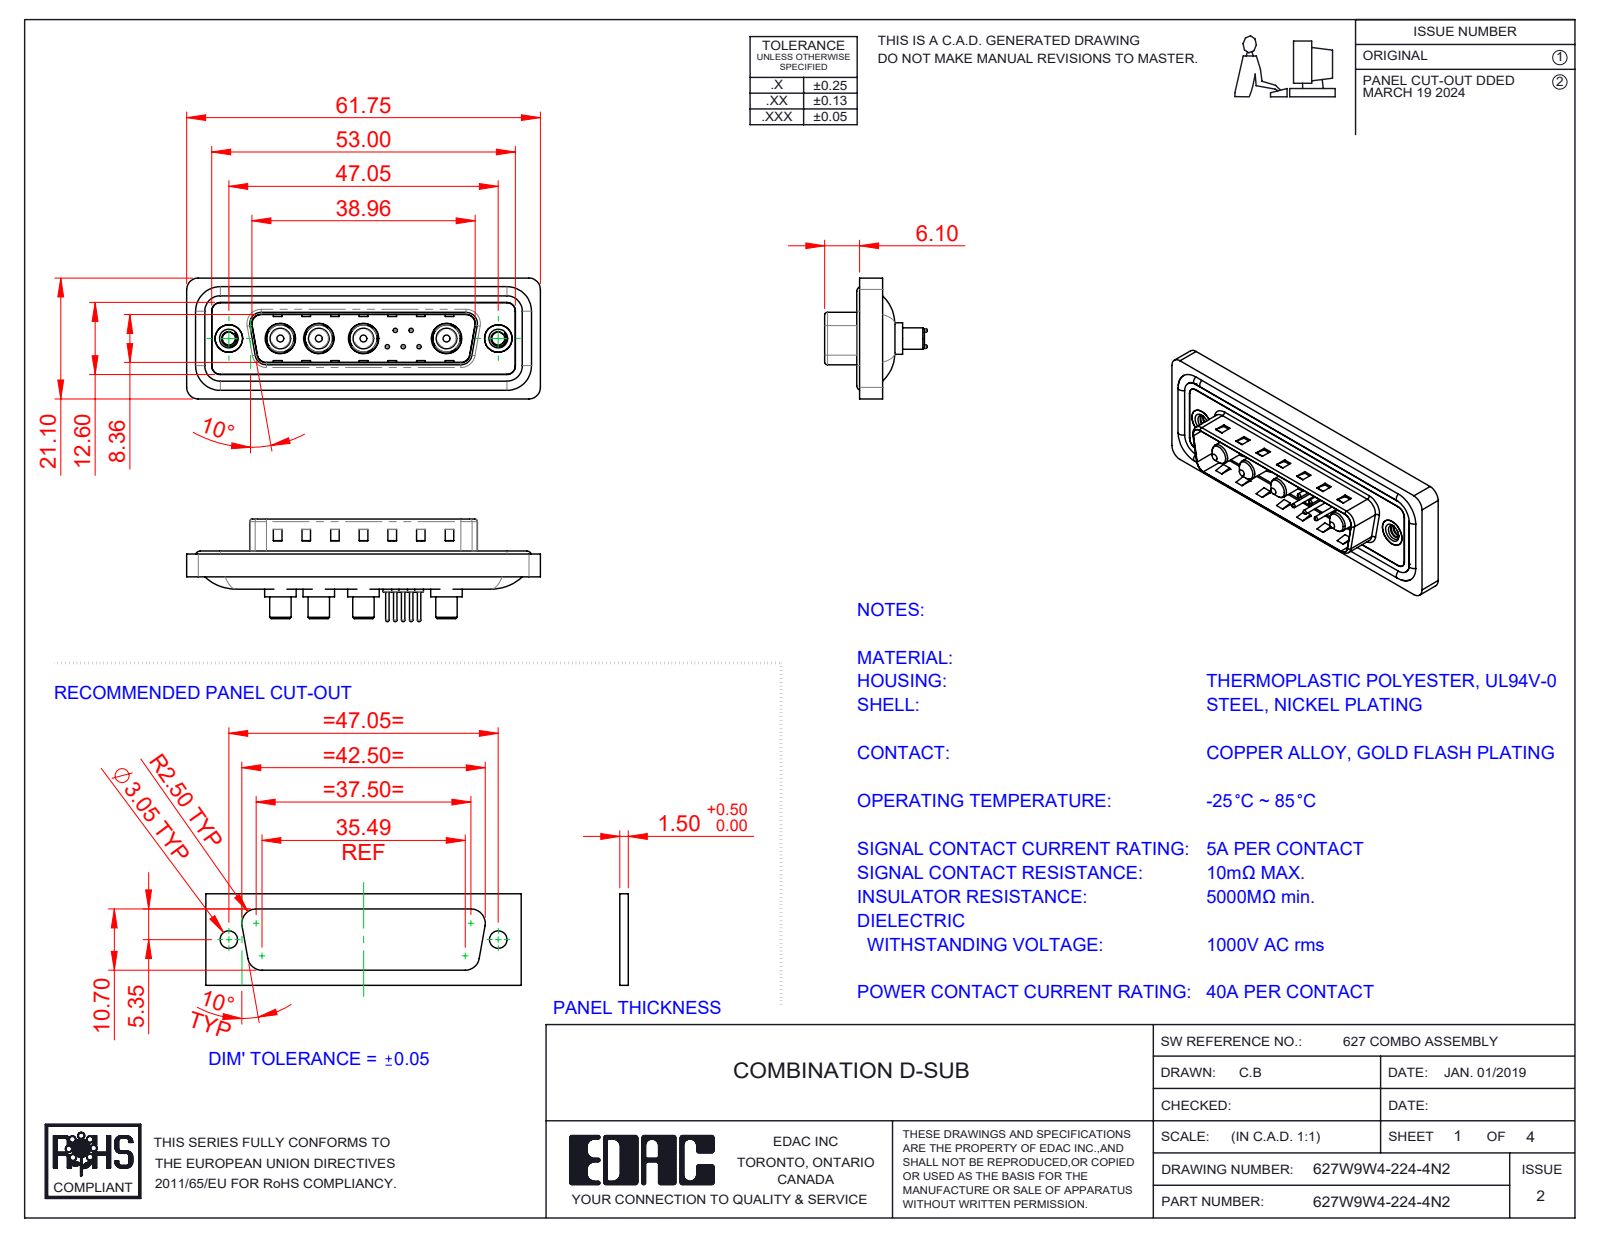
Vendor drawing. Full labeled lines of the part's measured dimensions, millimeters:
Part name (STEP PRODUCT): 627Combo Shell Rear_25 Contacts; Power Pin_40A S; 627Combo Contact Row 1_24; 627Combo Shell Front_25 Contacts (+5 more)
STEP written by: SolidWorks 2023 (CONFIG_CONTROL_DESIGN)
Units: millimetres
Bodies: 20 solids, 824 faces (284 planar, 334 cylindrical, 206 other)
Overall size (bounding box): 61.75 × 21.1 × 17.9
Volume: 7 478 mm³ · Surface area: 11 879 mm²
Round holes (diameter × count): ⌀0.75 ×5, ⌀1.6 ×5, ⌀2 ×5, ⌀4.85 ×4, ⌀5.3 ×4, ⌀2.26 ×2, ⌀4 ×2, ⌀4.8 ×2, ⌀5 ×2
Round bosses / shafts (diameter × count): ⌀1.5 ×5, ⌀0.6 ×5, ⌀5.5 ×4, ⌀5.2 ×4, ⌀4.75 ×4, ⌀3.75 ×4, ⌀3.6 ×4, ⌀1.6 ×4
Partial cylindrical surfaces — rounded edges, fillets, slot ends (radius × count): R1.5 ×22, R2 ×18, R0.5 ×8, R1.6 ×8, R0.25 ×4, R0.6 ×4, R0.65 ×4, R0.9 ×4
Main face-to-face distances: 0.4, 1.5, 1.1, 0.5, 1.6, 3.1, 2.9, 0.82, 9.58, 5.65
Hole centre spacings: 3.16, 2.77, 5.04, 14.51, 2.78, 4.4, 4.41, 5
